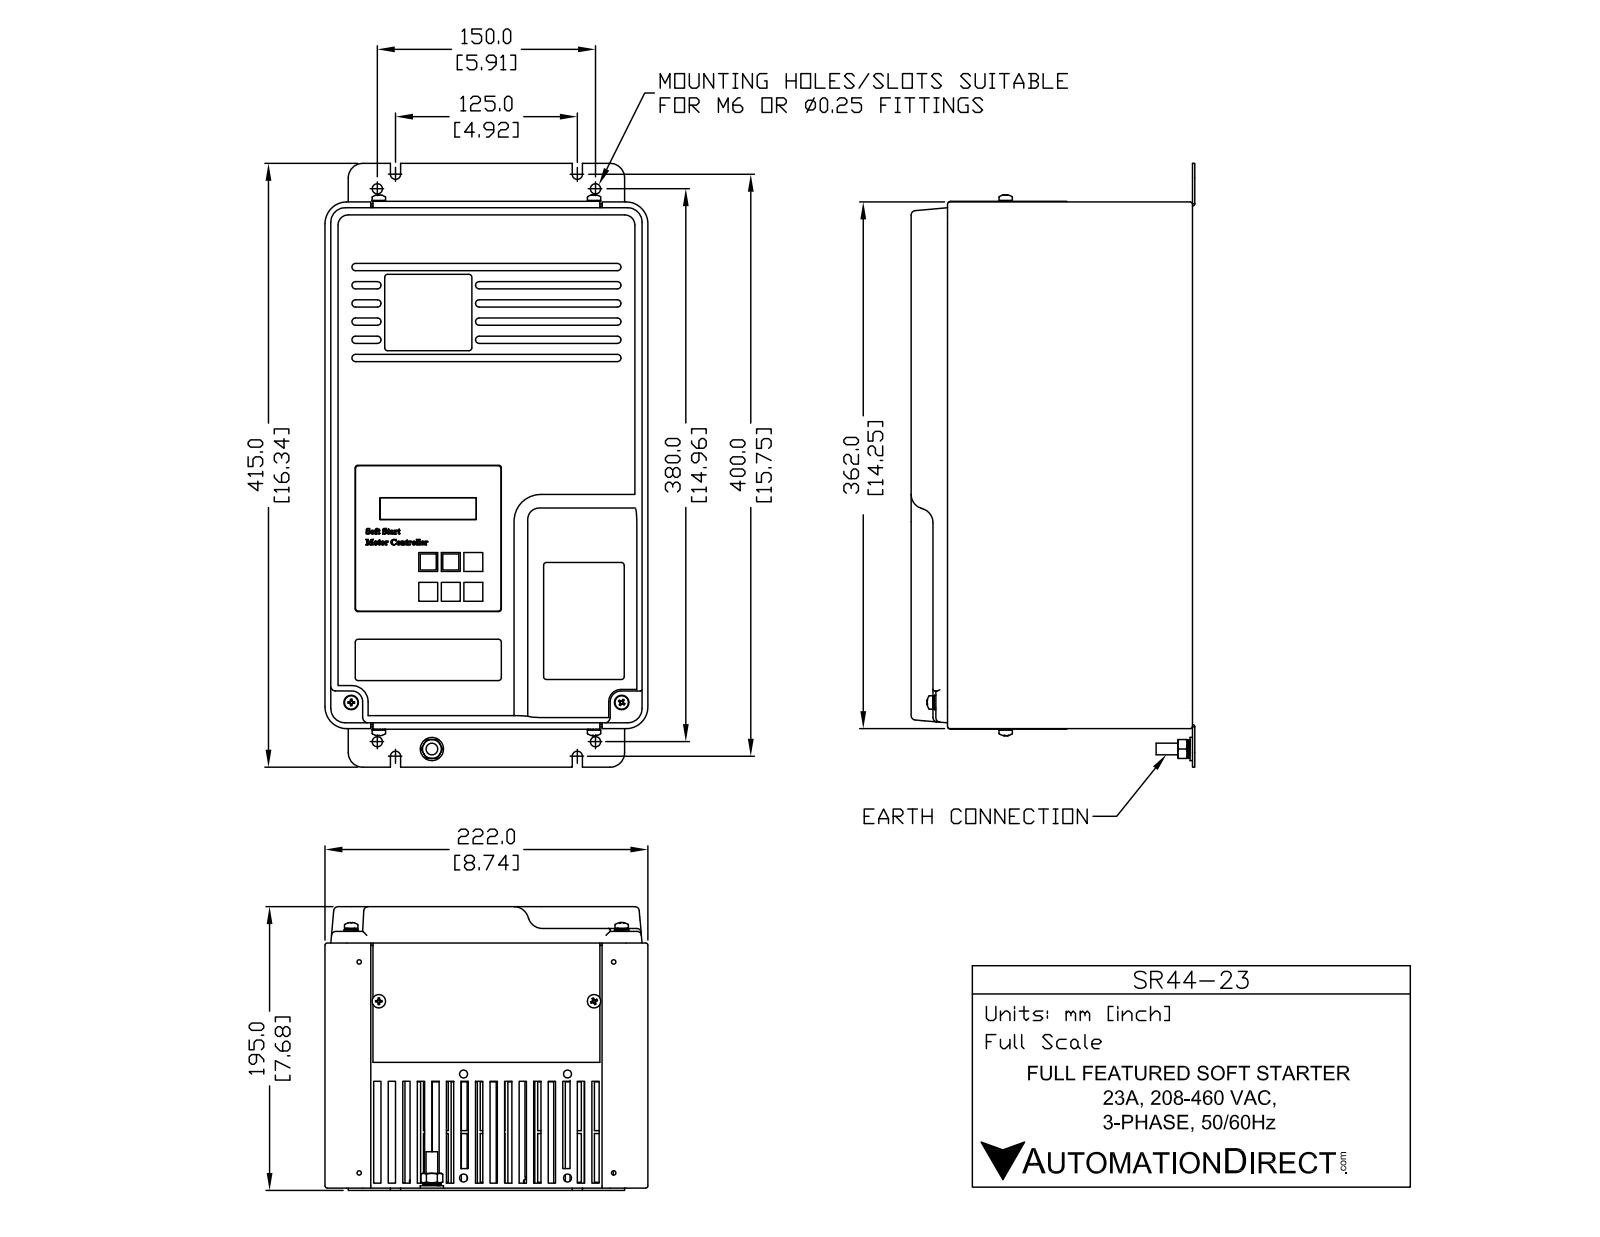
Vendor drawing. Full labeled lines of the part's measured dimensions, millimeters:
Part name (STEP PRODUCT): SR44-23
STEP written by: SolidWorks 2013 (AUTOMOTIVE_DESIGN)
Units: millimetres
Bodies: 1 solid, 768 faces (455 planar, 175 cylindrical, 138 other)
Overall size (bounding box): 415 × 222 × 194.7
Volume: 8 231 000 mm³ · Surface area: 711 054 mm²
Round holes (diameter × count): ⌀7 ×4
Round bosses / shafts (diameter × count): ⌀10 ×4, ⌀16 ×1, ⌀8 ×1
Partial cylindrical surfaces — rounded edges, fillets, slot ends (radius × count): R2.5 ×30, R2.4 ×28, R2.49 ×12, R1.5 ×11, R3 ×8, R10 ×8, R2 ×6, R3.5 ×4
Main face-to-face distances: 10.19, 20.38, 30.57, 40.76, 50.95, 61.14, 71.33, 5.9, 81.52, 216.1
Hole centre spacings: 150, 380, 408.53
